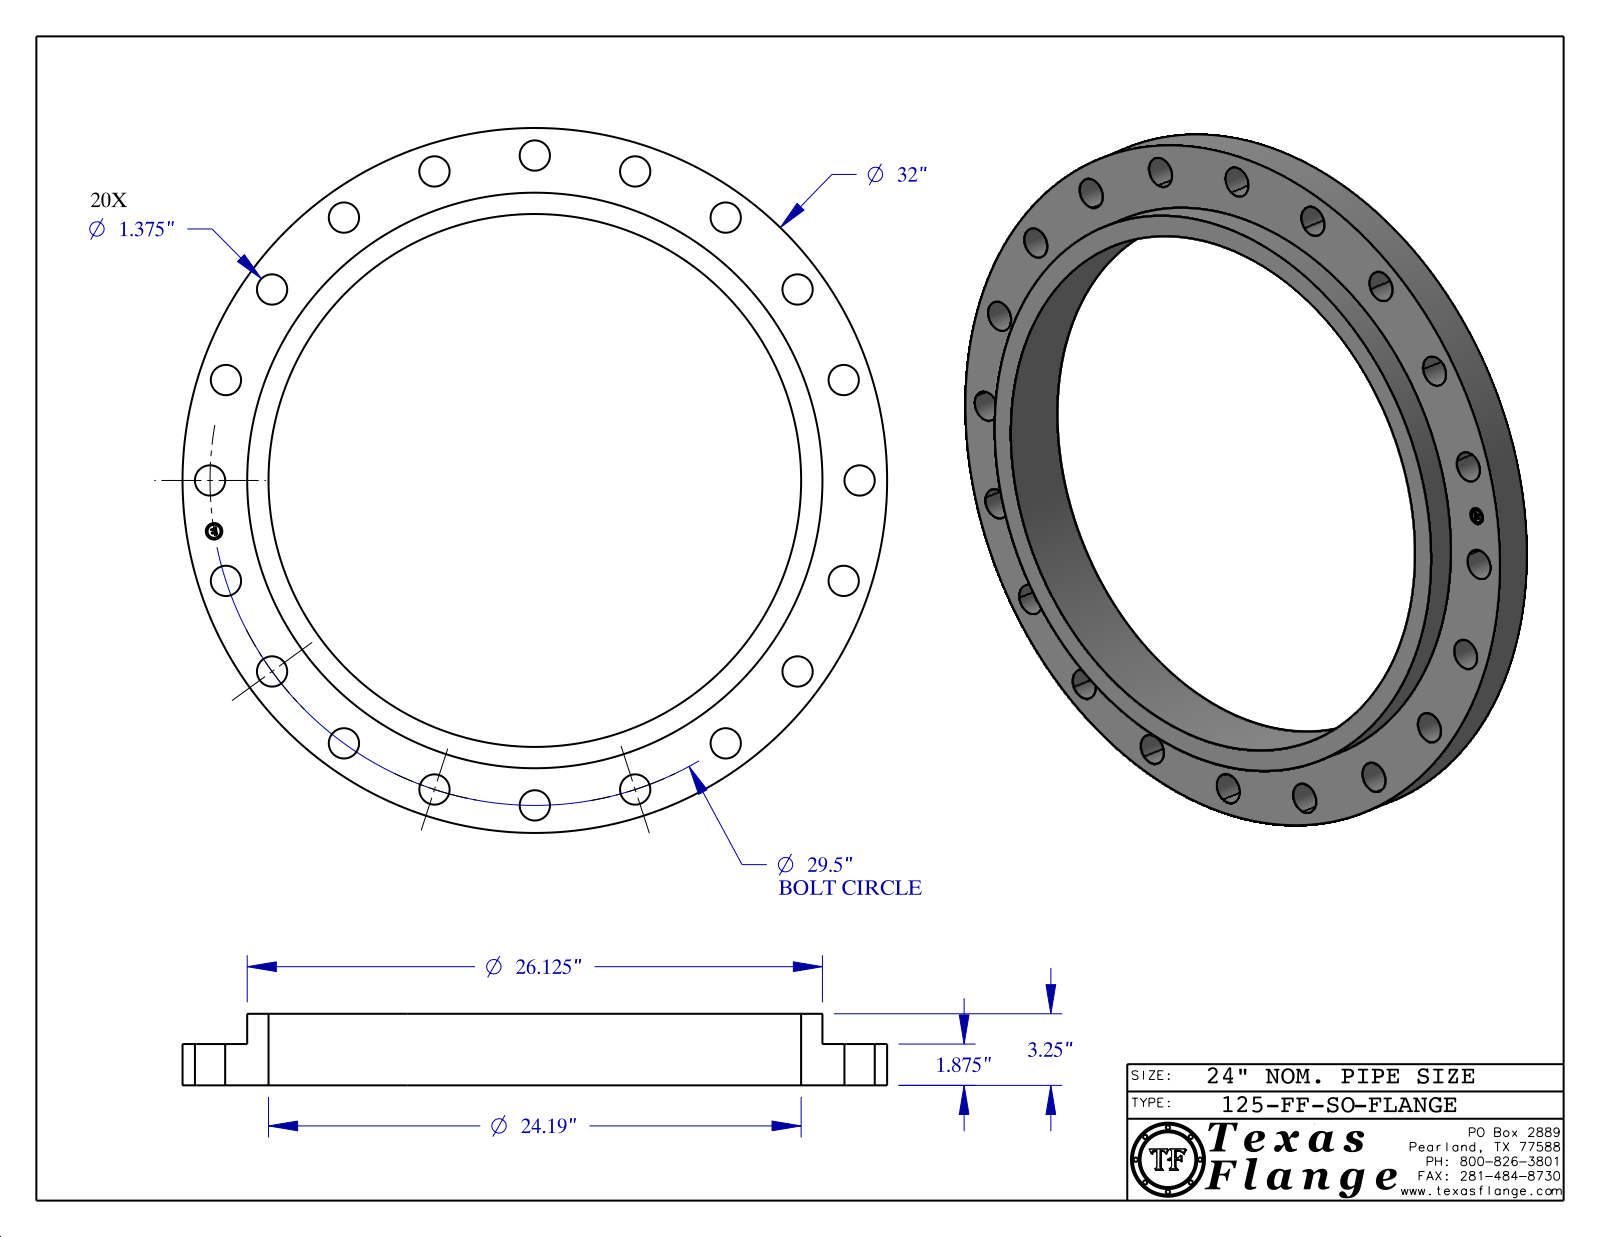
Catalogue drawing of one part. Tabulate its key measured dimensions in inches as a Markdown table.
| quantity | value |
| --- | --- |
| part name | 125-FF-SO-B16.1 |
| STEP written by | CATIA V5 STEP AP214 (AUTOMOTIVE_DESIGN) |
| units | inches |
| bodies | 1 solid, 434 faces (368 planar, 66 cylindrical, 0 other) |
| overall size | 32 × 32 × 3.25 |
| volume | 695.7 in³ |
| surface area | 1 340 in² |
| round holes (diameter × count) | 1.375 × 20, 0.75 × 1, 24.19 × 1 |
| round bosses / shafts (diameter × count) | 0.045 × 8, 32 × 1, 26.125 × 1, 0.591 × 1 |
| main face-to-face distances | 1.875, 3.25, 1.375, 1.86, 0.015, 1.39, 0.224, 0.219, 0.041, 0.145 |
| hole center spacings | 14.75, 29.137, 4.615, 17.34, 20.859, 23.866, 26.285, 9.116 |
